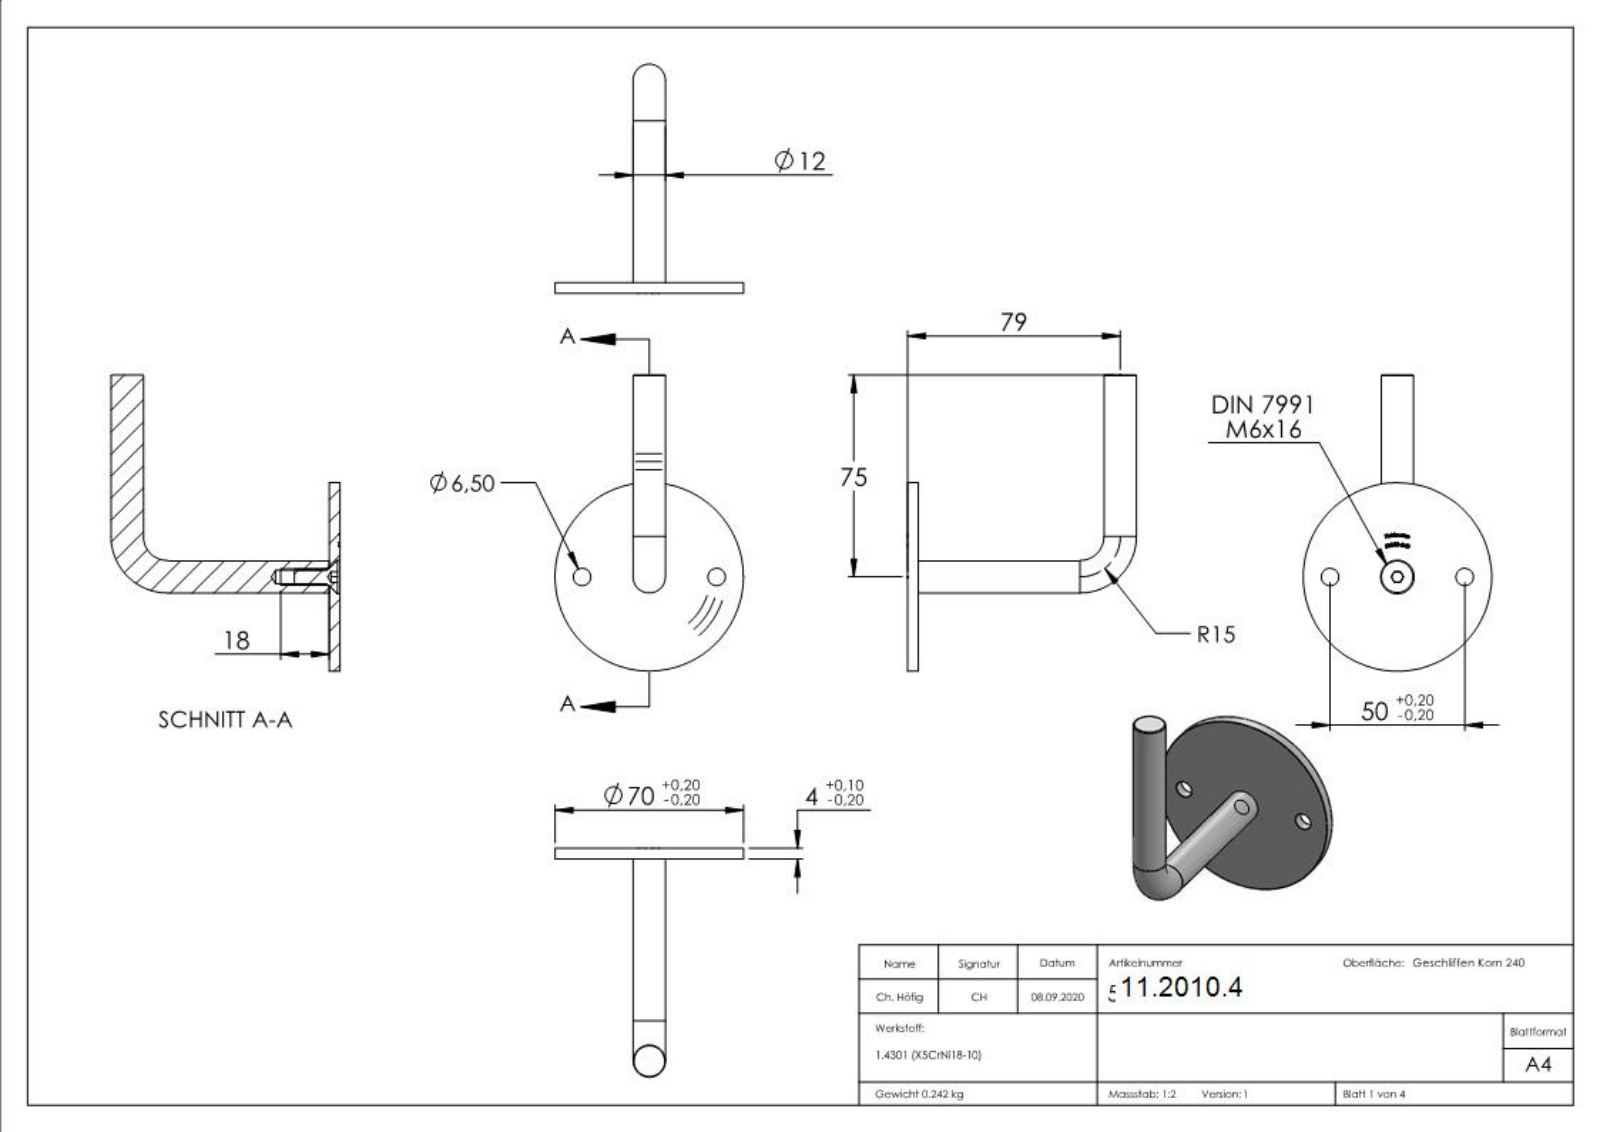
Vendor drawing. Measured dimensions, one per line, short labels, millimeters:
name: socket countersunk head screw_din; 50300-240 Teil2; 50300-240; socket countersunk head screw_din_DIN 7991 - M6 x 16 --- 9.7S (+3 more)
written by: SolidWorks 2018 (CONFIG_CONTROL_DESIGN)
unit: mm
bodies: 3 solids, 337 faces (129 planar, 38 cylindrical, 170 other)
size: 165.82 × 110 × 70
volume: 31 113 mm³; area: 15 223 mm²
holes: 2× ⌀6.5, 1× ⌀5, 1× ⌀12.5
bosses: 2× ⌀12, 1× ⌀70, 1× ⌀11.57, 1× ⌀6
face distances: 4, 49.36, 53.36, 84.82, 35.46, 31.46, 16, 33.36, 37.36, 68.82
hole spacings: 25, 50
